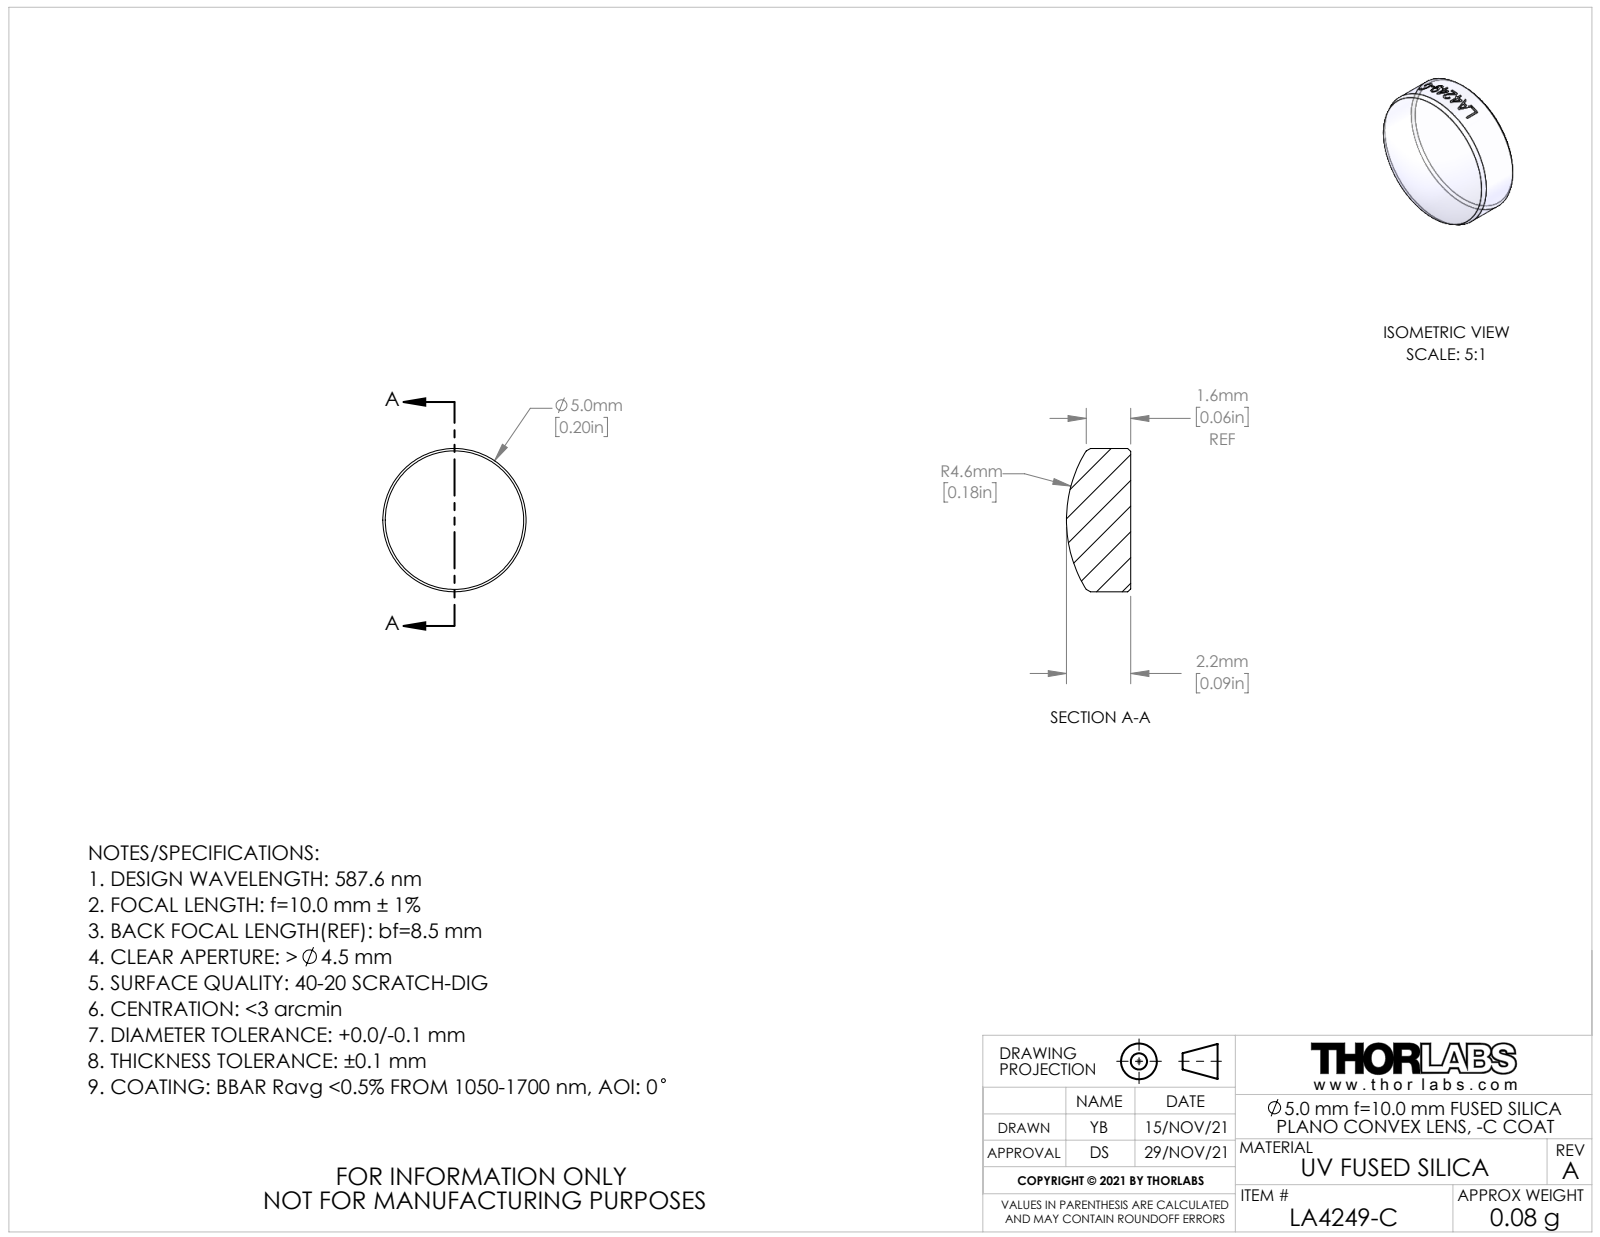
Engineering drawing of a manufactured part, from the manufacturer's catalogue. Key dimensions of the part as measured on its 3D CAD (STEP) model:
Part name (STEP PRODUCT): CTN018127; CTN018059-E0W
STEP written by: SolidWorks 2018 (AUTOMOTIVE_DESIGN)
Units: millimetres
Bodies: 1 solid, 21 faces (1 planar, 14 cylindrical, 6 other)
Overall size (bounding box): 5 × 5 × 2.24
Volume: 37 mm³ · Surface area: 63 mm²
Round bosses / shafts (diameter × count): ⌀5 ×1
